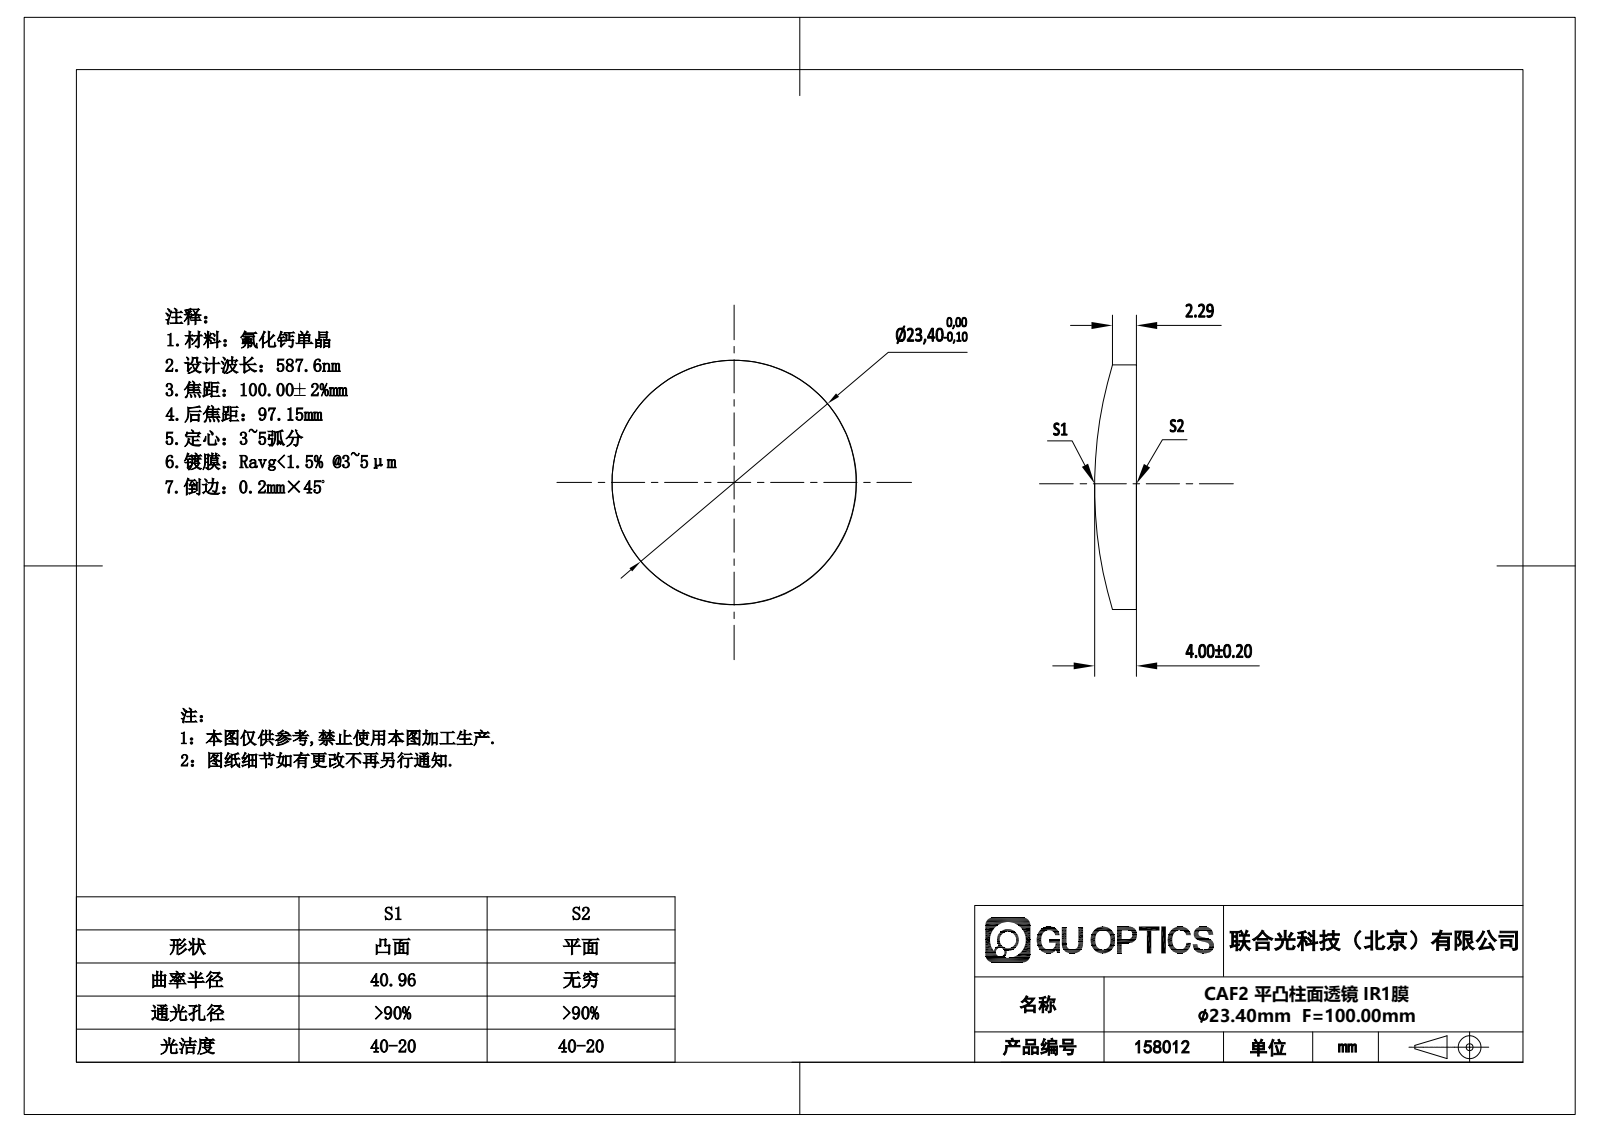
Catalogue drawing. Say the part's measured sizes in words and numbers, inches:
The part is named "GL55-025-100-IR1". Its 3-D file was written by "SolidWorks 2022 (AUTOMOTIVE_DESIGN)". It is 1 solid with 9 faces: 1 planar, 4 cylindrical and 4 other. Overall it measures 0.921 by 0.921 by 0.157 inches. Its volume is 0.093 cubic inches and its surface area 1.674 square inches. Round bosses or shafts: 1 of diameter 0.921. Partial cylindrical surfaces (rounded edges, fillets, slot ends): 1 of radius 1.613.
